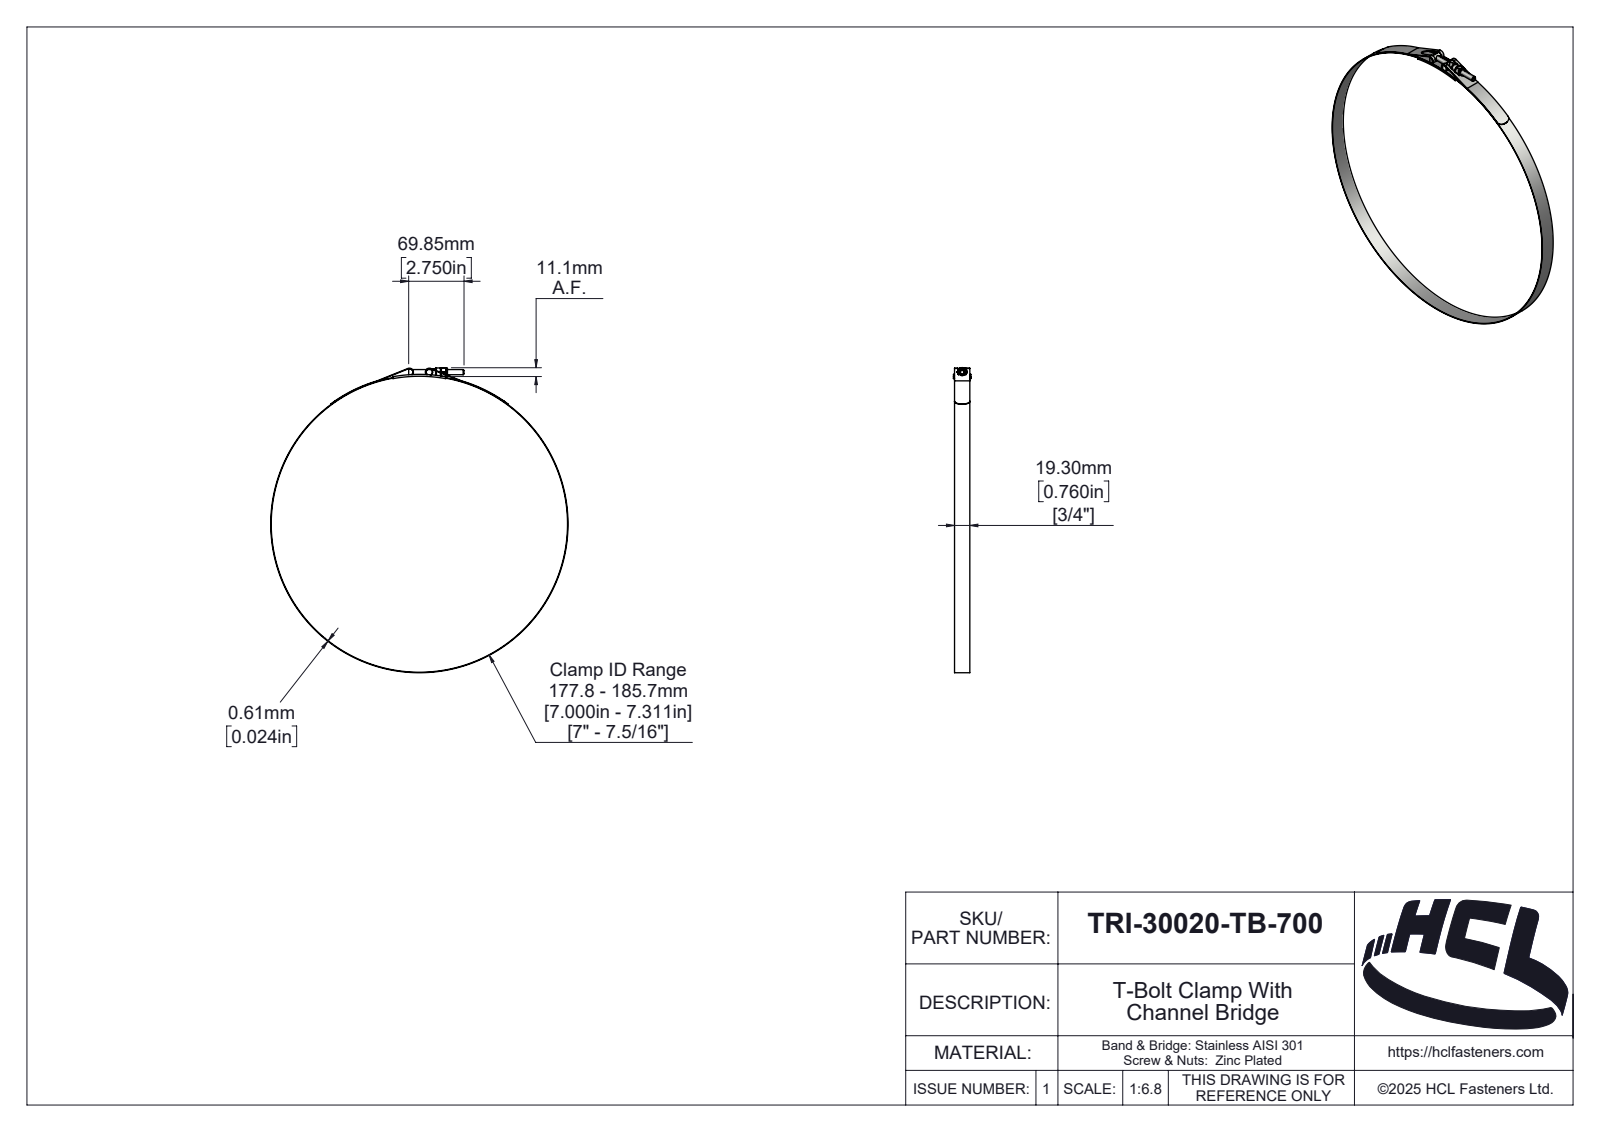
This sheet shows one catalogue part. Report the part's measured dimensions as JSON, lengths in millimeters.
{"part_name": "TRI-30020-TB-700", "step_written_by": "SolidWorks 2025 (AUTOMOTIVE_DESIGN)", "units": "millimeters", "bodies": {"solids": 6, "faces": 330, "planar": 44, "cylindrical": 122, "other": 164}, "overall_size": [384.92, 375.22, 22], "volume_mm3": 21222, "surface_area_mm2": 62147, "round_holes": [[5.4, 1], [6.35, 1], [6.5, 1], [7.58, 1], [374, 1]], "round_bosses_or_shafts": [[8.58, 2], [375.22, 1], [10.58, 1]], "partial_cylinders_radius": [[0.39, 6], [0.5, 2], [4.39, 2], [5, 2], [0.59, 1], [2.42, 1], [3.03, 1], [3.19, 1]], "face_to_face_distances": [0.61, 19.3, 1.35, 20.65, 0.74, 21.39, 20.04, 22, 20.78, 11.11], "hole_center_spacings": [192]}
